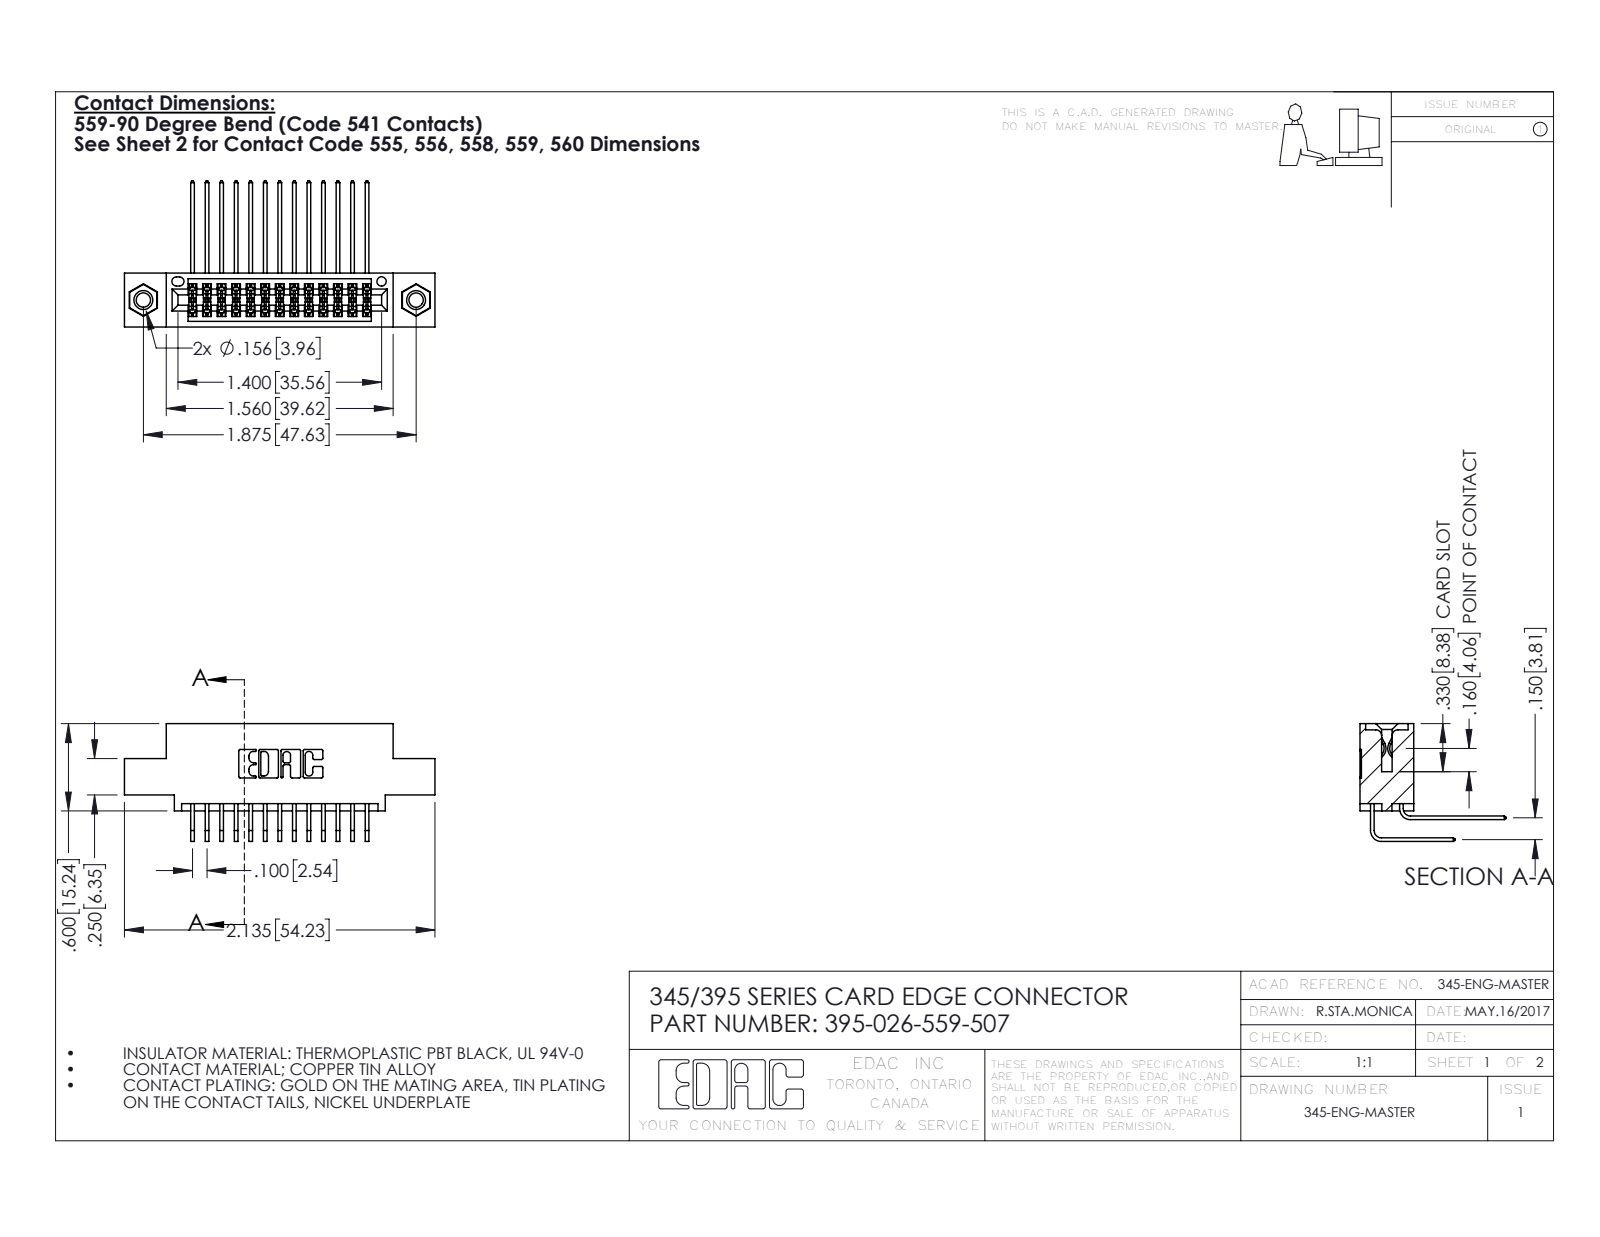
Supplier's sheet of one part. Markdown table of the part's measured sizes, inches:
| quantity | value |
| --- | --- |
| part name | 345-250-001_345-250-005-103; 345-292-001_558 559 Tail - 1; 345-292-001_559 Tail - 2; 345 Part_0.110 Offset - 0.156 Dia-TI (+1 more) |
| STEP written by | SolidWorks 2016 (CONFIG_CONTROL_DESIGN) |
| units | inches |
| bodies | 29 solids, 1542 faces (1026 planar, 500 cylindrical, 16 other) |
| overall size | 2.135 × 1.005 × 0.809 |
| volume | 0.309 in³ |
| surface area | 12.01 in² |
| round holes (diameter × count) | 0.098 × 2, 0.125 × 2, 0.156 × 2, 0.064 × 1 |
| round bosses / shafts (diameter × count) | 0.155 × 2 |
| partial cylindrical surfaces (radius × count) | 0.006 × 39, 0.01 × 22, 0.007 × 6, 0.031 × 6, 0.026 × 3, 0.014 × 2, 0.019 × 2, 0.022 × 2 |
| main face-to-face distances | 0.072, 0.298, 0.2, 0.37, 0.098, 0.272, 0.025, 0.225, 0.15, 0.1 |
| hole center spacings | 0.27, 1.643, 1.875 |
